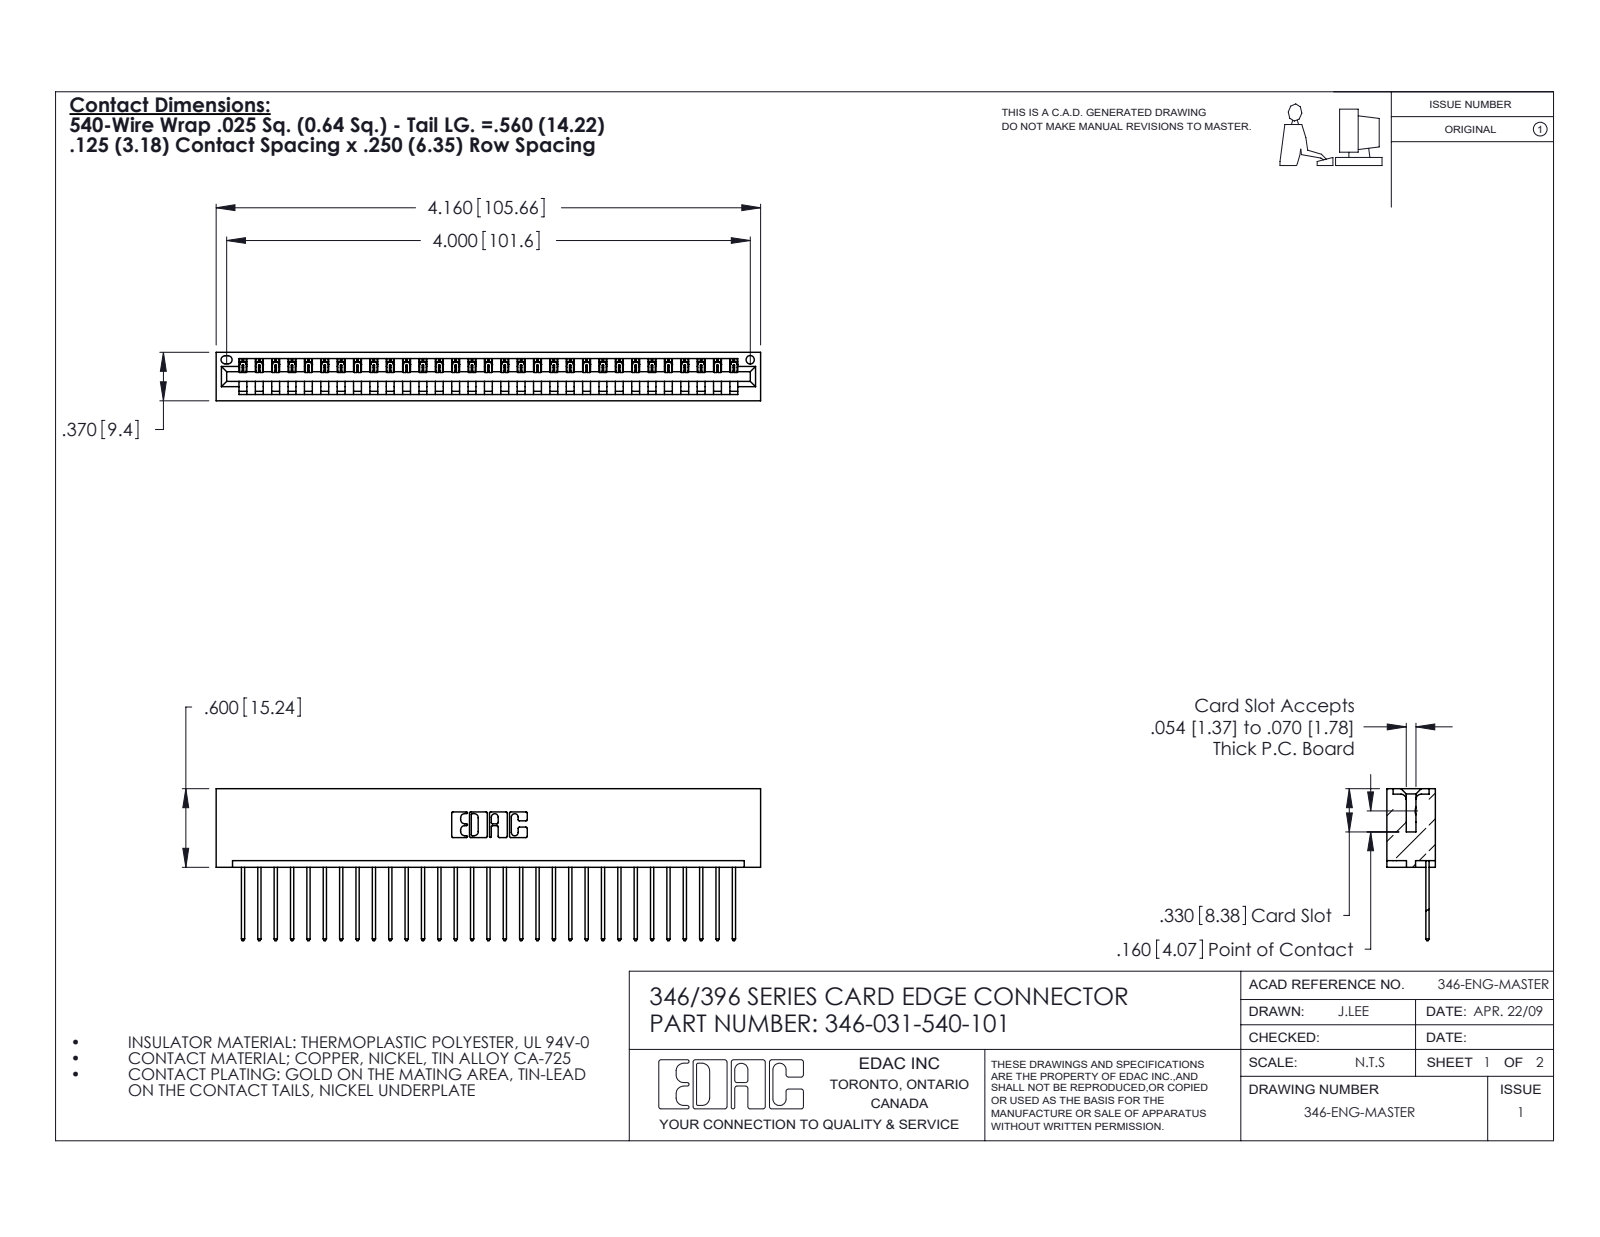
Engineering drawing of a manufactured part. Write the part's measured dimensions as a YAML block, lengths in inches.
part_name: "346-031-540-101; 346 Part_No Mounting Lugs; 345-292-001_345-293-140"
step_written_by: "SolidWorks 2020 (CONFIG_CONTROL_DESIGN)"
units: inches
bodies: {solids: 32, faces: 1912, planar: 1312, cylindrical: 600, other: 0}
overall_size: [4.16, 1.16, 0.37]
volume: 0.649
surface_area: 21
round_holes:
  - {diameter: 0.064, count: 1}
partial_cylinders:
  - {radius: 0.006, count: 62}
  - {radius: 0.01, count: 62}
  - {radius: 0.01, count: 22}
  - {radius: 0.007, count: 6}
  - {radius: 0.031, count: 6}
  - {radius: 0.026, count: 3}
  - {radius: 0.031, count: 2}
  - {radius: 0.04, count: 2}
face_to_face_distances: [0.048, 0.322, 0.25, 0.37, 0.072, 0.298, 0.025, 0.148, 0.222, 0.1]
